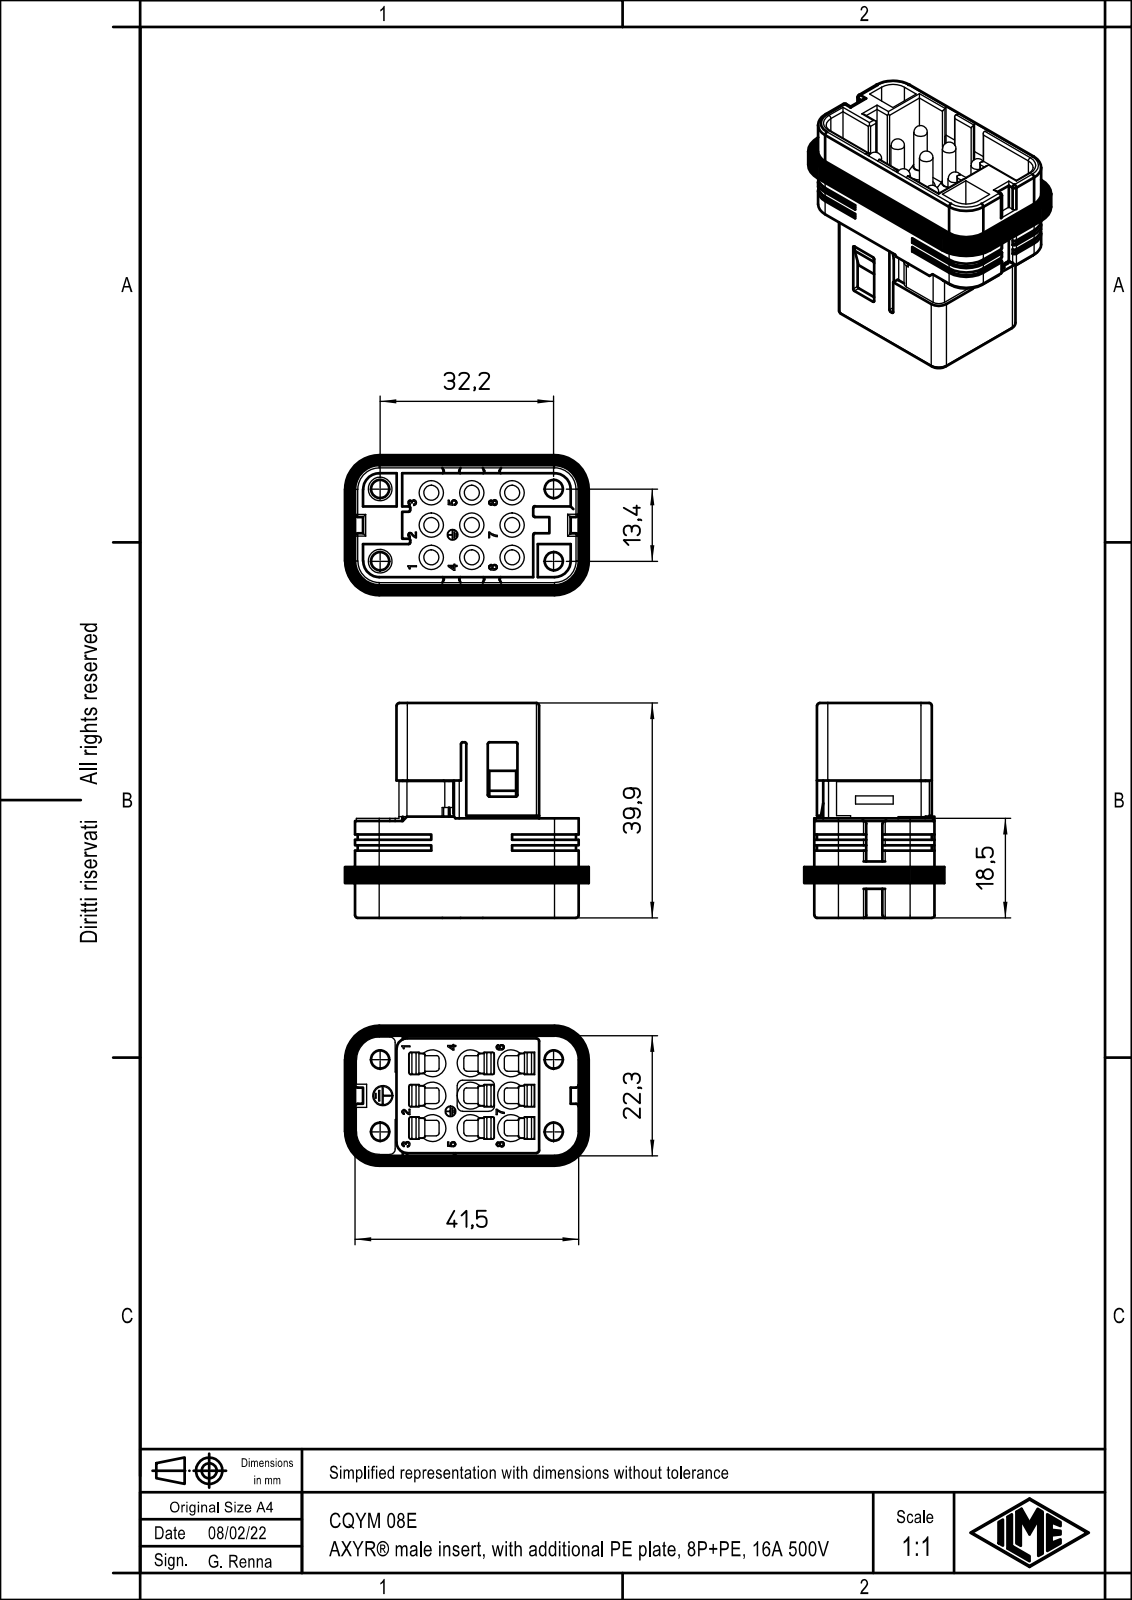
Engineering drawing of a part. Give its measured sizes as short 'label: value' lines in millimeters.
name: CQYM_08E
written by: Creo Elements/Direct Modeling 20.1B 02-Apr-2019 (C) Parametric Technology GmbH (AUTOMOTIVE_DESIGN)
unit: mm
bodies: 1 solid, 1556 faces (960 planar, 455 cylindrical, 141 other)
size: 45.2 × 39.9 × 26
volume: 17 298 mm³; area: 14 555 mm²
holes: 4× ⌀3.4, 1× ⌀2
bosses: 9× ⌀4.5, 9× ⌀2.5, 1× ⌀1.81
rounds: 59× R0.2, 58× R0.5, 48× R0.4, 44× R0.3, 18× R0.1, 15× R1, 9× R2.5, 6× R2
face distances: 0.5, 1, 1.5, 21.8, 20.8, 20.3, 7.15, 14.15, 21.3, 7.35
hole spacings: 13.4, 32.2, 34.88, 14.31, 15.91, 19.38, 20.59
